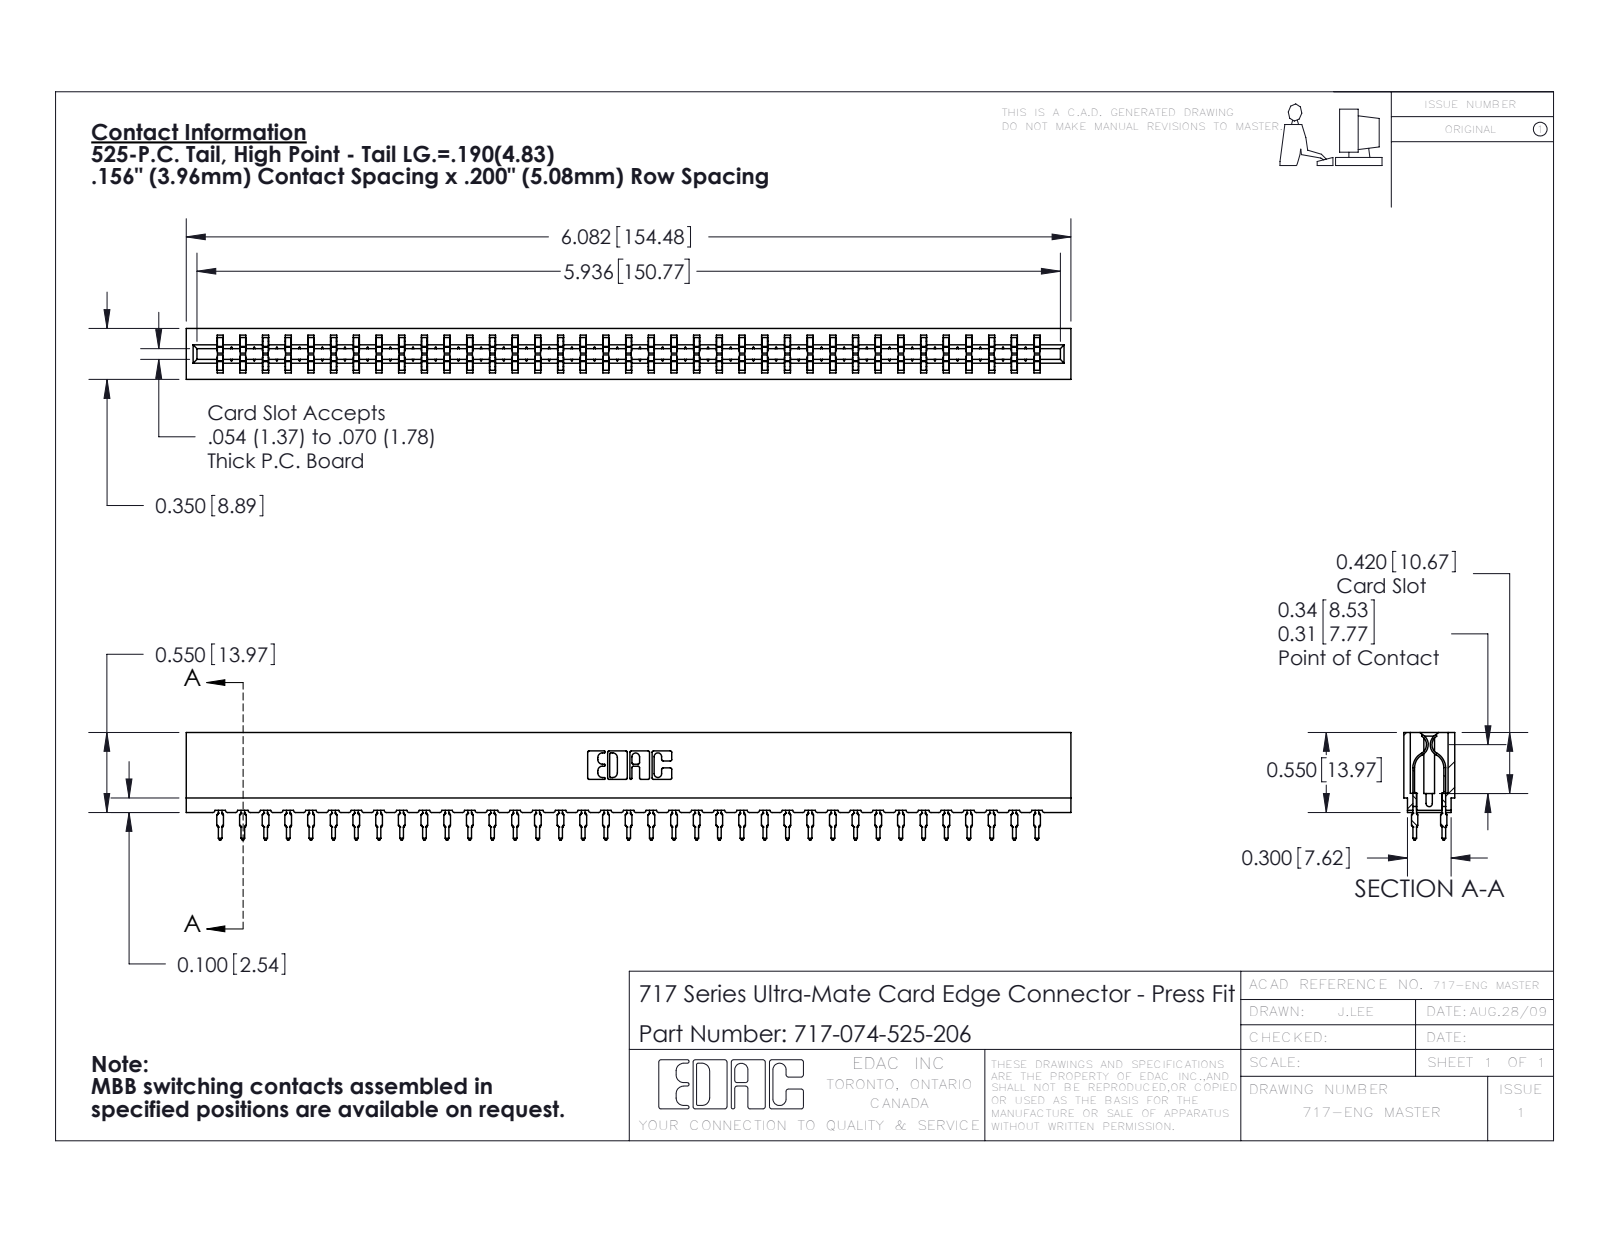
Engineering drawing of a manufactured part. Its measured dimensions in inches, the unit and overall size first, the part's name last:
Units: inches
Overall size (bounding box): 6.082 × 0.739 × 0.35
Partial cylindrical surfaces — rounded edges, fillets, slot ends (radius × count): R0.021 ×148, R0.015 ×74, R0.01 ×22, R0.005 ×8, R0.011 ×8, R0.007 ×6, R0.031 ×6, R0.026 ×3
Main face-to-face distances: 0.212, 0.138, 0.35, 0.063, 0.287, 0.076, 0.149, 0.074, 0.045, 0.305
Volume: 0.817 in³ · Surface area: 31.51 in²
Bodies: 75 solids, 6754 faces (3495 planar, 1335 cylindrical, 1924 other)
Part name (STEP PRODUCT): 717-074-525-206; 745-292-001_525; 717 Part_Insulator Option - 06
STEP written by: SolidWorks 2016 (CONFIG_CONTROL_DESIGN)
